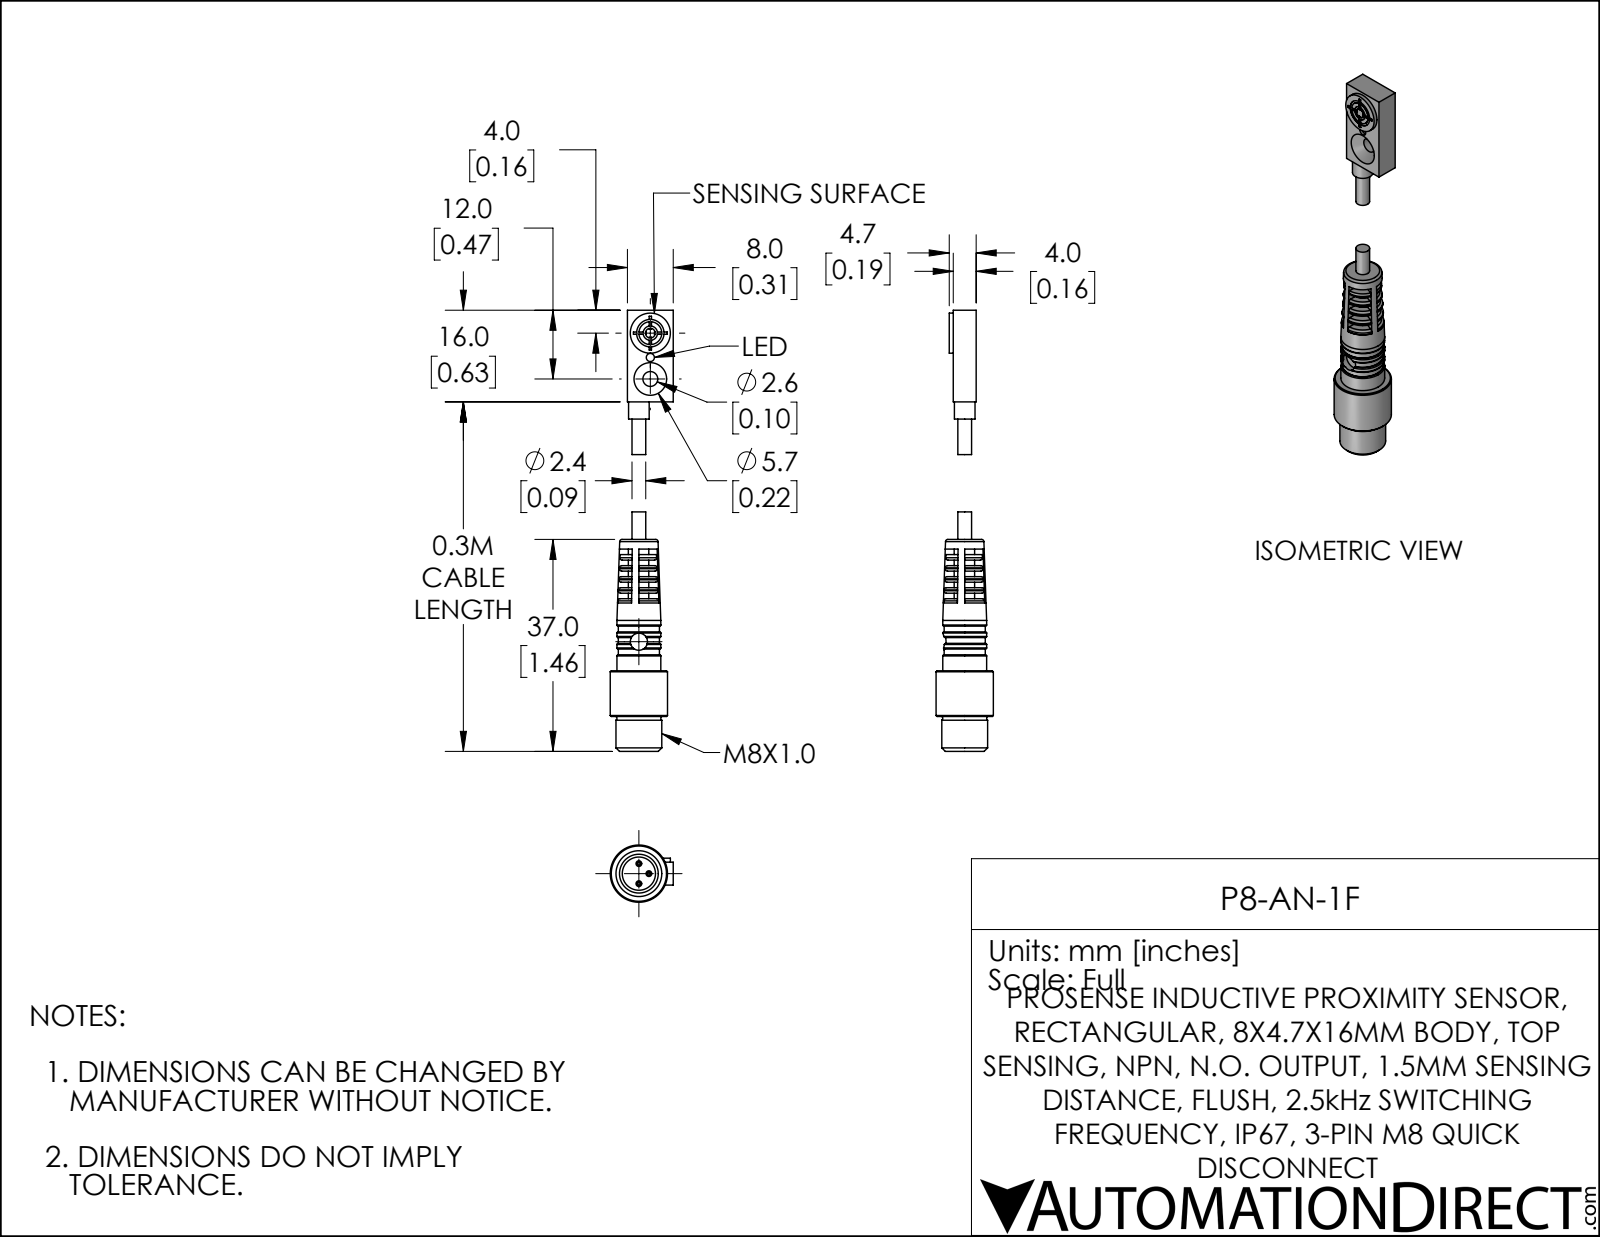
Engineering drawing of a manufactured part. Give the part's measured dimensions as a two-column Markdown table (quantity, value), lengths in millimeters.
| quantity | value |
| --- | --- |
| part name | P8-AN-1F_1; P8-AN-1F_2; P8-AN-1F |
| STEP written by | SolidWorks 2019 (AUTOMOTIVE_DESIGN) |
| units | millimeters |
| bodies | 2 solids, 240 faces (116 planar, 56 cylindrical, 68 other) |
| overall size | 76.7 × 11 × 10 |
| volume | 2 210 mm³ |
| surface area | 2 039 mm² |
| round holes (diameter × count) | 1.4 × 1, 2.5 × 1, 2.6 × 1, 3 × 1, 4.8 × 1, 5.8 × 1 |
| round bosses / shafts (diameter × count) | 1 × 3, 10 × 1, 8 × 1, 7.7 × 1, 7.2 × 1, 7 × 1, 4 × 1, 3.6 × 1 |
| partial cylindrical surfaces (radius × count) | 0.8 × 1, 1.8 × 1 |
| main face-to-face distances | 1, 3.9, 2.9, 8, 4, 1.9, 1.9, 4.8, 7.7, 6.7 |
| hole center spacings | 3.8, 4.2, 8 |
